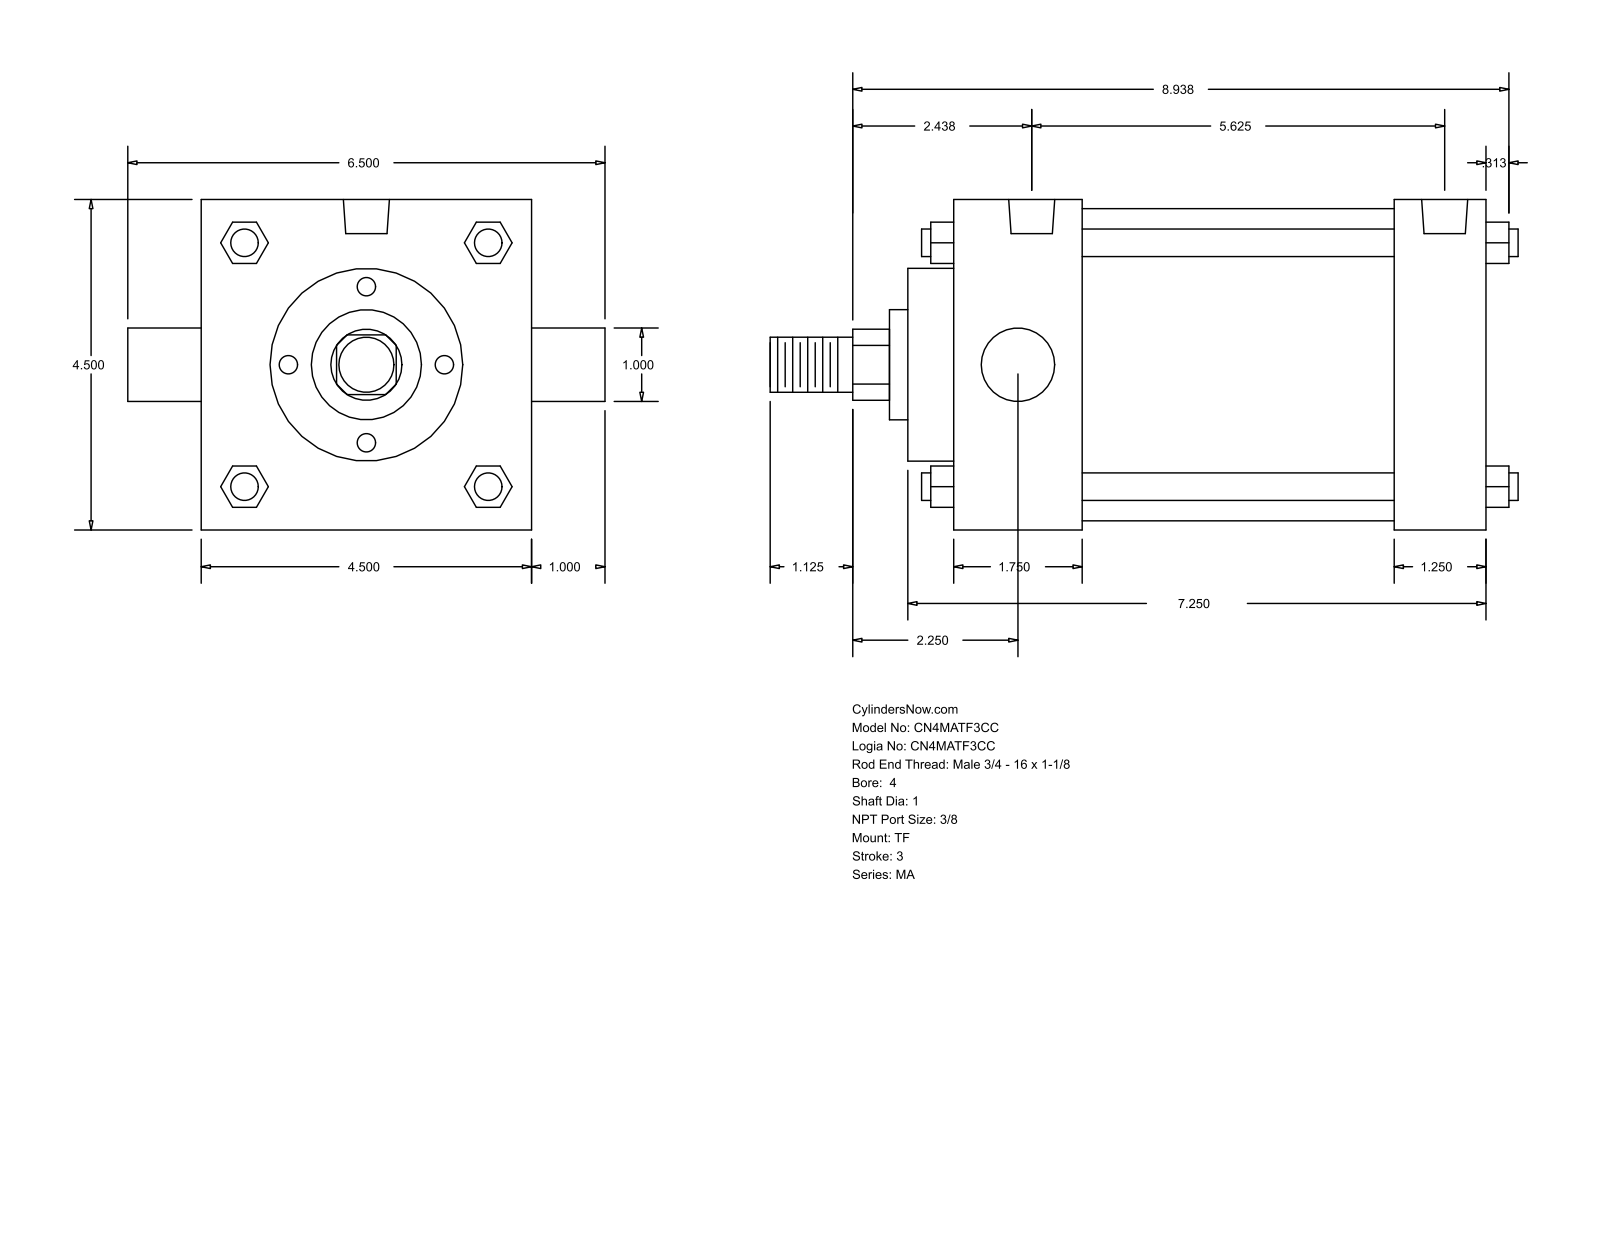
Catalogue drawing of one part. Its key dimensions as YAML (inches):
part_name: "MA_TF__0400_1"
step_written_by: "GSSL Pune (CONFIG_CONTROL_DESIGN)"
units: inches
bodies: {solids: 0, faces: 122, planar: 93, cylindrical: 29, other: 0}
overall_size: [10.187, 6.5, 4.5]
round_holes:
  - {diameter: 0.437, count: 3}
  - {diameter: 0.627, count: 2}
round_bosses_or_shafts:
  - {diameter: 0.375, count: 4}
  - {diameter: 1, count: 2}
  - {diameter: 4.25, count: 1}
  - {diameter: 2.625, count: 1}
  - {diameter: 1.5, count: 1}
  - {diameter: 0.75, count: 1}
partial_cylinders:
  - {radius: 0.484, count: 1}
face_to_face_distances: [4.5, 7.25, 6, 1.25, 1.75, 4.25, 5.5, 7.875, 0.625, 2.375]
hole_center_spacings: [0.187, 5.438, 5.25, 5.625]
